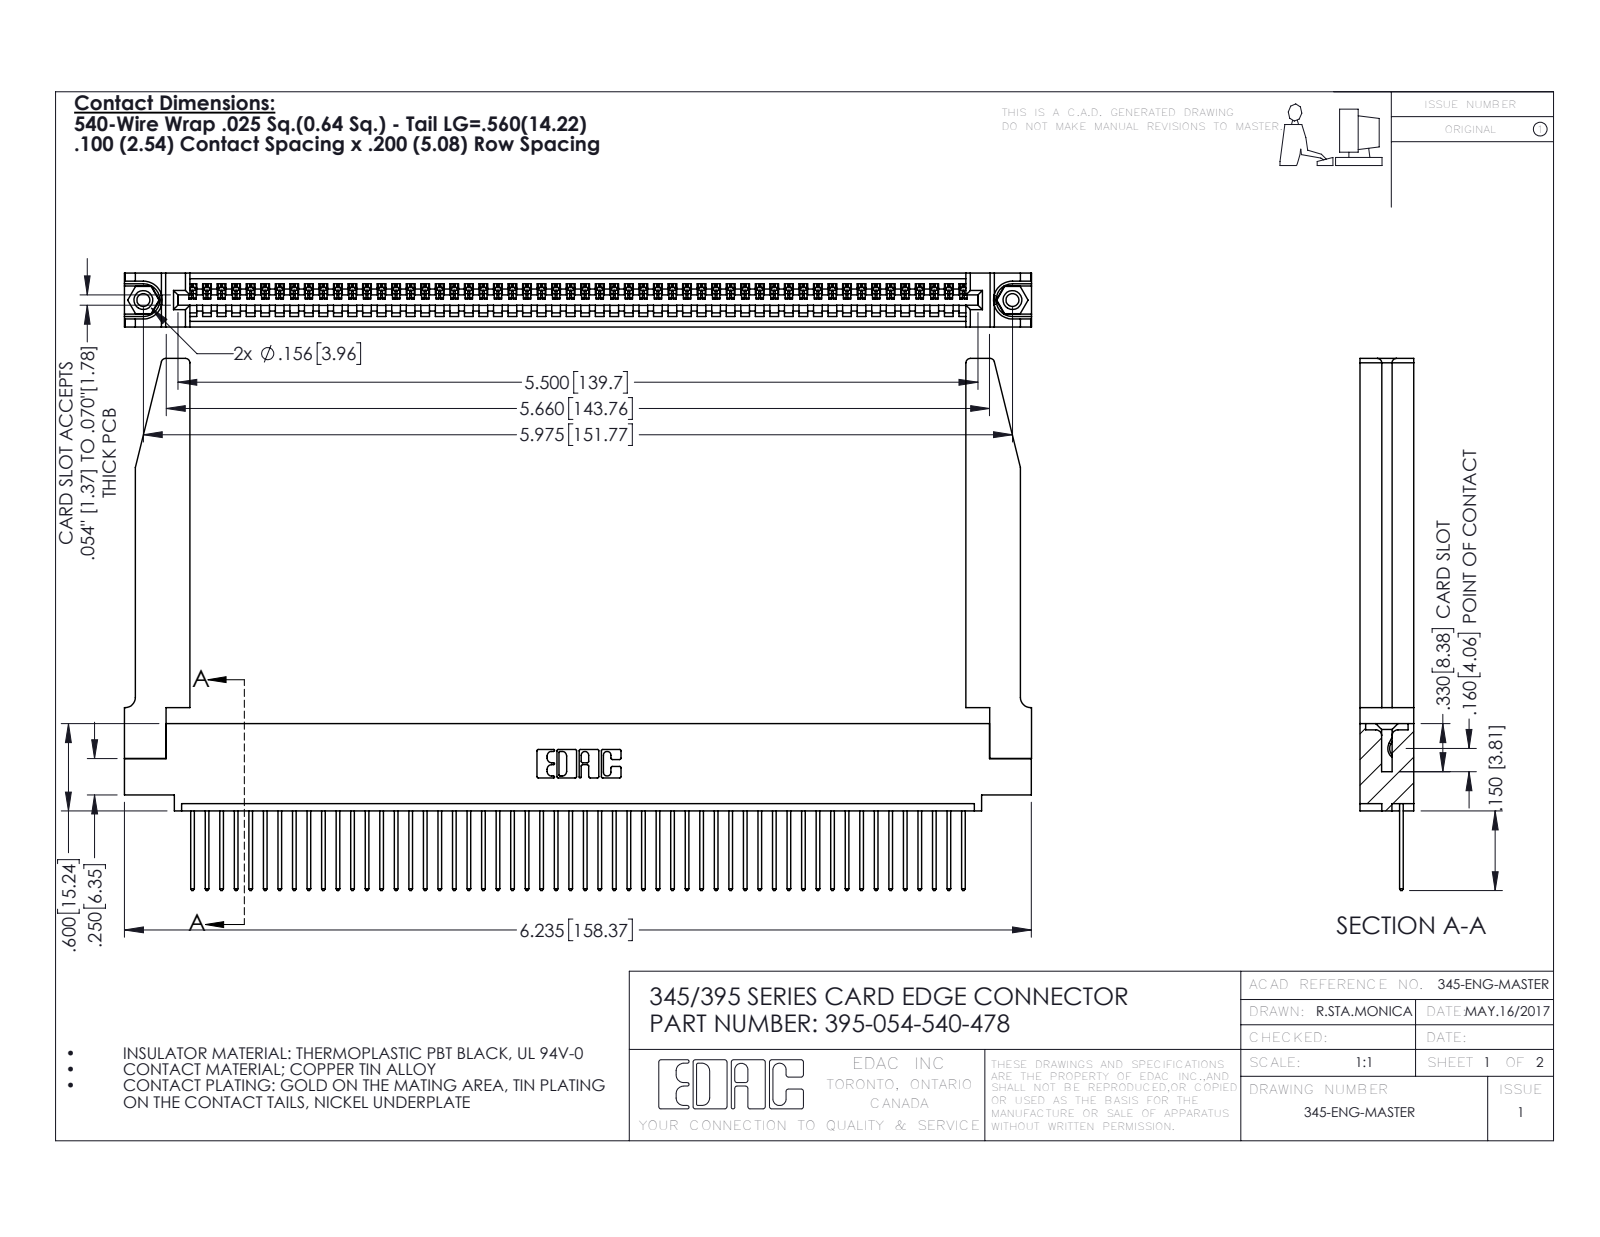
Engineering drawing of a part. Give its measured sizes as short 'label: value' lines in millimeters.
name: 345-250-001_345-250-001-102; 395-054-540-478; 345-292-001_345-293-140; 345 Part_0.110 Offset - 0.156 Dia-TH (+1 more)
written by: SolidWorks 2016 (CONFIG_CONTROL_DESIGN)
unit: mm
bodies: 59 solids, 3496 faces (2386 planar, 1058 cylindrical, 52 other)
size: 158.4 × 92.9 × 9.4
volume: 22 910 mm³; area: 27 740 mm²
holes: 2× ⌀2.3, 2× ⌀3.2, 2× ⌀4, 1× ⌀1.6
bosses: 2× ⌀3.9
rounds: 108× R0.2, 108× R0.3, 22× R0.3, 8× R0.8, 6× R0.2, 6× R0.8, 3× R0.7, 2× R0.8
face distances: 1.8, 9.4, 7.6, 2.5, 6.9, 0.6, 5.1, 5.7, 3.8, 3.8
hole spacings: 6.9, 145.8, 151.8
